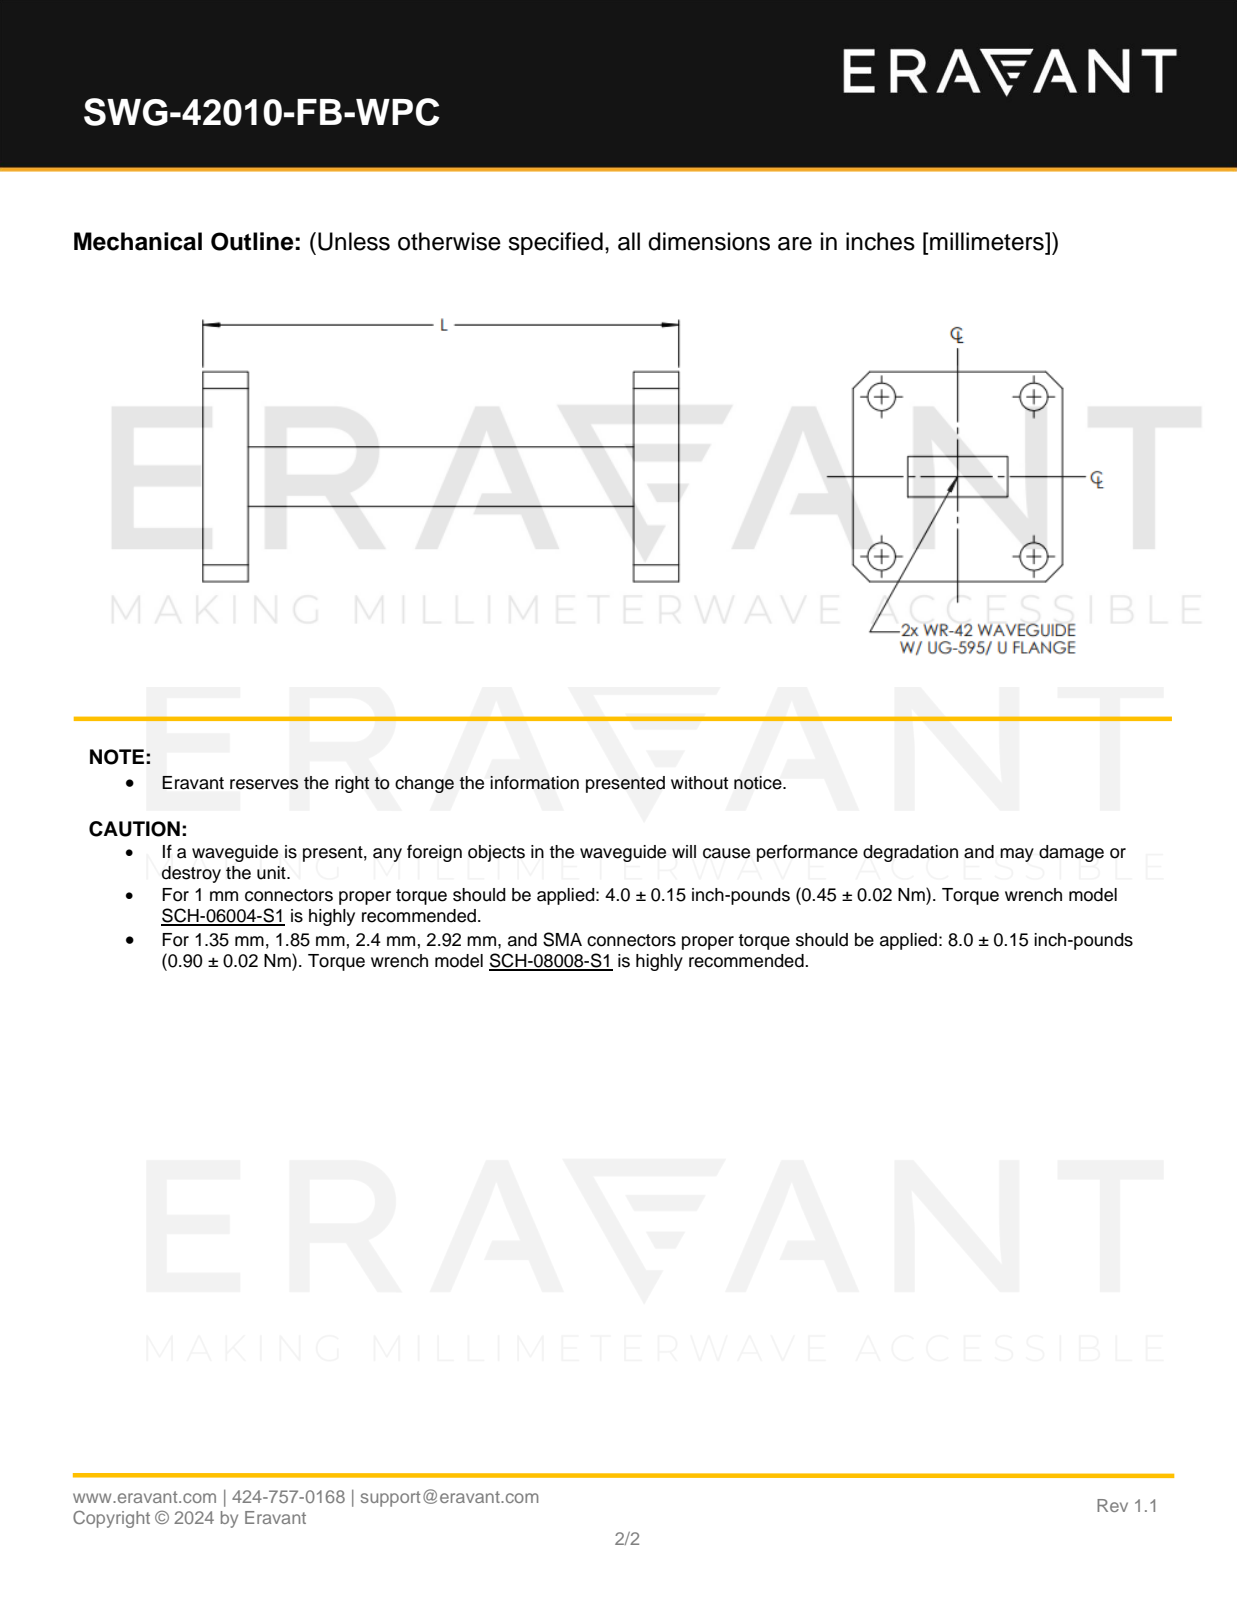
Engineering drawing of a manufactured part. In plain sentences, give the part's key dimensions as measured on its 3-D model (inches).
The part is named "SWG-42010-F1". Its 3-D file was written by "SolidWorks 2013 (CONFIG_CONTROL_DESIGN)". It is 1 solid with 44 faces: 28 planar, 16 cylindrical and 0 other. Overall it measures 1 by 0.88 by 0.88 inches. Its volume is 0.281 cubic inches and its surface area 6.436 square inches. Round holes: 4 of diameter 0.116. The main face-to-face distances are 0.19, 0.81, 1, 0.04, 0.21, 0.62, 0.315, 0.355, 0.525, 0.565. The hole center spacings are 0.64, 0.67, 0.927.
